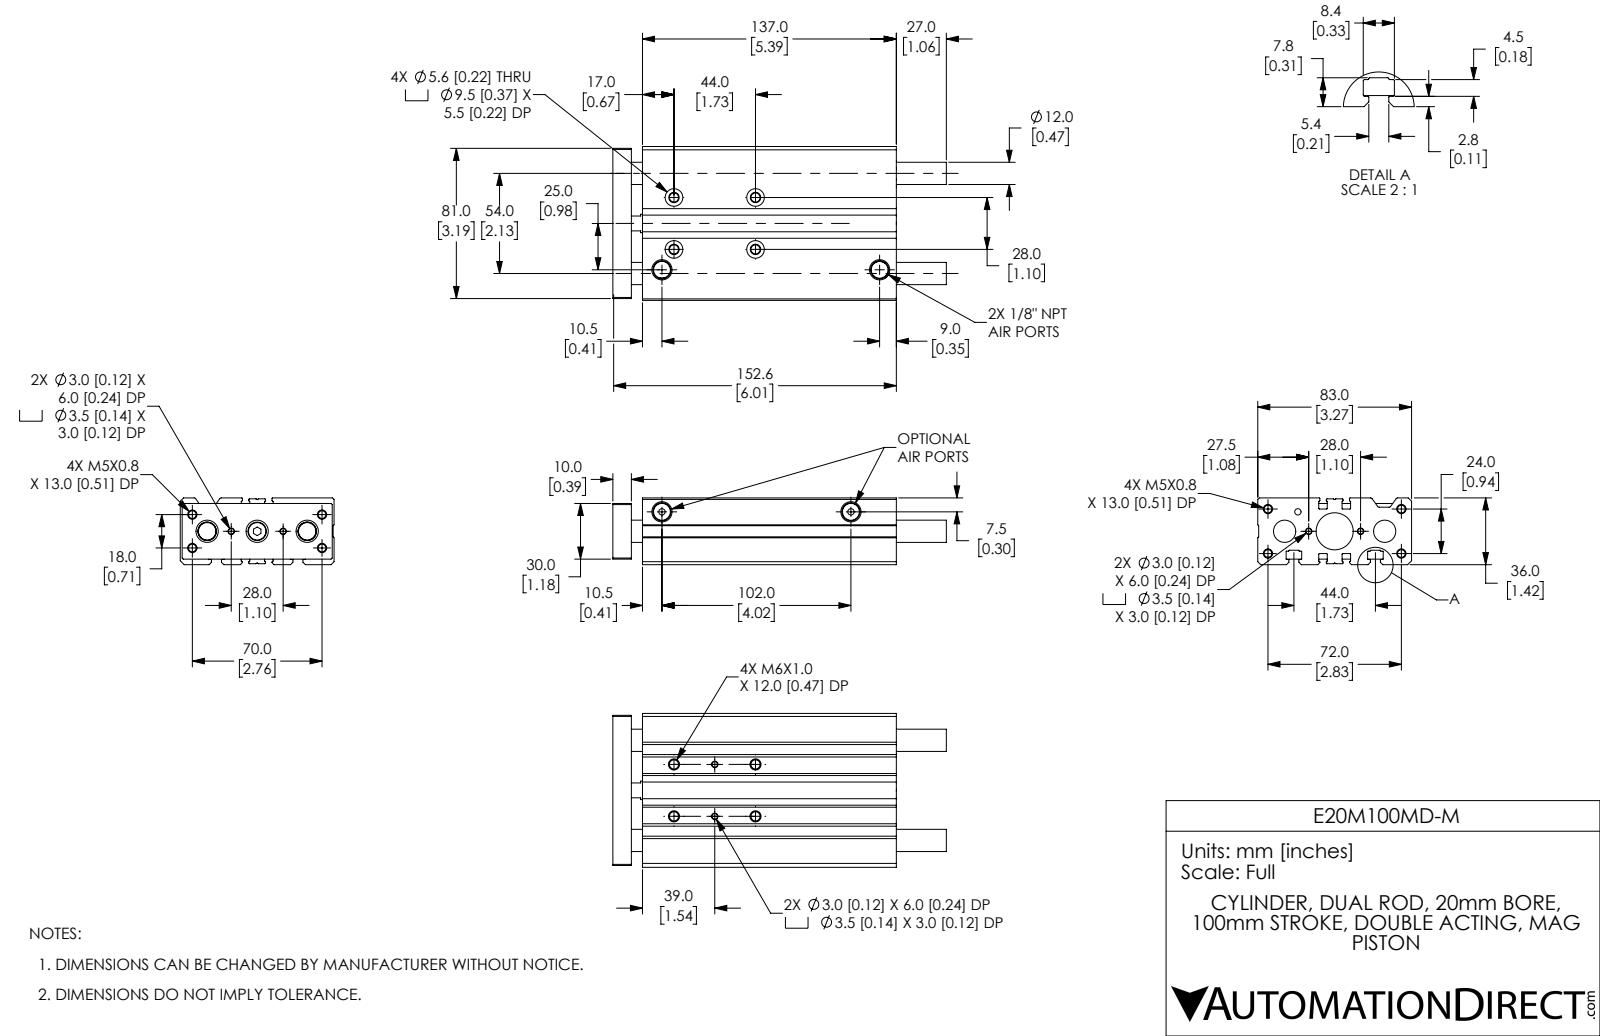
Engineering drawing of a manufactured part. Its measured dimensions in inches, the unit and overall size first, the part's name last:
Units: inches
Overall size (bounding box): 7.087 × 3.268 × 1.417
Round holes (diameter × count): ⌀0.163 ×8, ⌀0.118 ×4, ⌀0.138 ×4, ⌀0.194 ×4, ⌀0.22 ×4, ⌀0.374 ×4, ⌀0.236 ×3, ⌀0.472 ×3, ⌀0.135 ×2, ⌀0.39 ×2, ⌀0.135 ×1, ⌀0.472 ×1
Round bosses / shafts (diameter × count): ⌀0.394 ×1, ⌀0.39 ×1
Partial cylindrical surfaces — rounded edges, fillets, slot ends (radius × count): R0.016 ×20, R0.008 ×18, R0.012 ×10, R0.01 ×8, R0.039 ×4
Main face-to-face distances: 1.417, 0.236, 0.02, 0.118, 3.268, 1.181, 0.874, 1.791, 0.63, 1.11
Hole centre spacings: 0.124, 0.474, 0.591, 0.828, 0.866, 0.9, 0.987, 1.102
Volume: 22.5 in³ · Surface area: 158.5 in²
Bodies: 5 solids, 405 faces (128 planar, 182 cylindrical, 95 other)
Part name (STEP PRODUCT): E20M100MD-M_BODY; E20M100MD-M_ENDPLATE; E20M100MD-M
STEP written by: SolidWorks 2019 (CONFIG_CONTROL_DESIGN)
